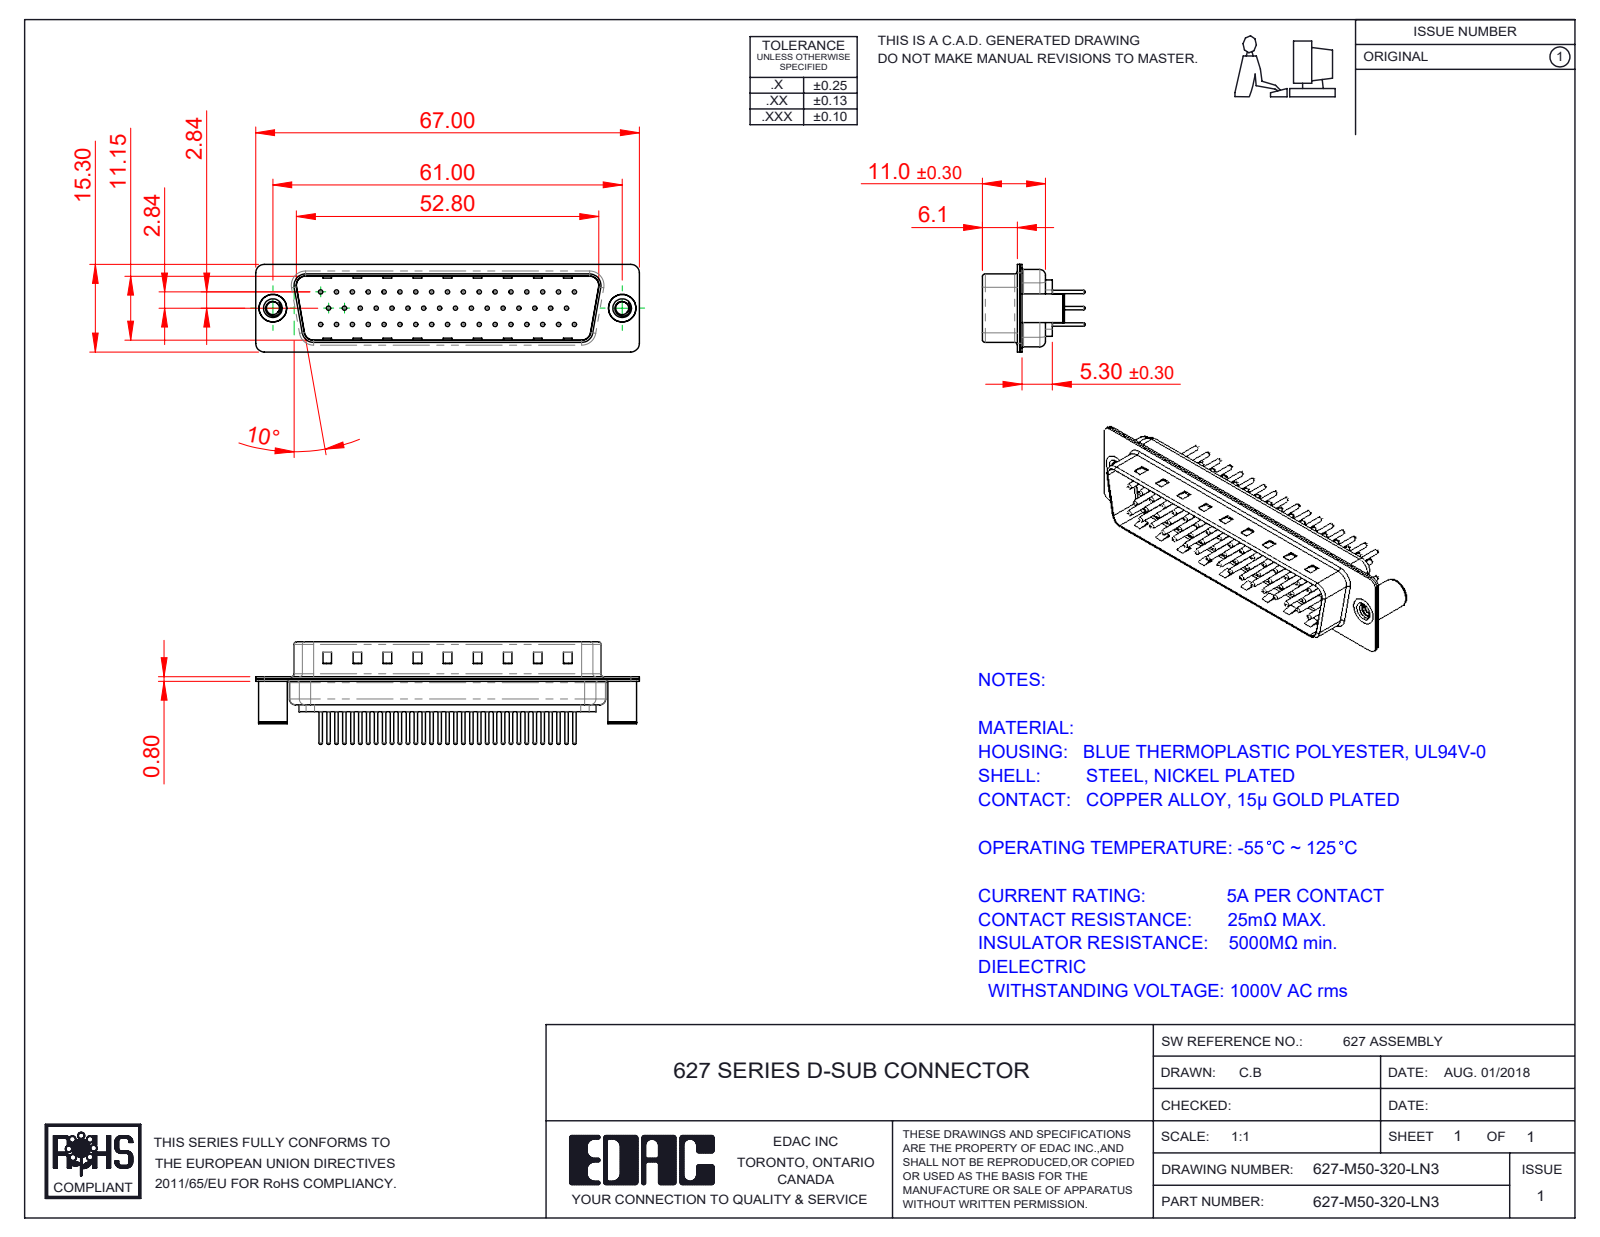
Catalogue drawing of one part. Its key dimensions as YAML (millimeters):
part_name: "627-M50-320-LN3; 627M Contact Row 3_20; 627M Shell Front_50 Contacts; 627M Contact Row 1_20 (+4 more)"
step_written_by: "SolidWorks 2020 (CONFIG_CONTROL_DESIGN)"
units: millimeters
bodies: {solids: 55, faces: 2296, planar: 553, cylindrical: 865, other: 878}
overall_size: [67, 17.9, 15.3]
volume: 4648
surface_area: 10957
round_holes:
  - {diameter: 0.75, count: 50}
  - {diameter: 1.6, count: 50}
  - {diameter: 2, count: 50}
  - {diameter: 2.26, count: 2}
  - {diameter: 3.26, count: 2}
  - {diameter: 4, count: 2}
  - {diameter: 4.8, count: 2}
round_bosses_or_shafts:
  - {diameter: 1.5, count: 50}
  - {diameter: 0.6, count: 50}
  - {diameter: 5, count: 2}
  - {diameter: 4.9, count: 2}
partial_cylinders:
  - {radius: 1.5, count: 16}
  - {radius: 2, count: 12}
  - {radius: 0.5, count: 8}
  - {radius: 1.6, count: 8}
  - {radius: 0.25, count: 4}
  - {radius: 0.6, count: 4}
  - {radius: 0.65, count: 4}
  - {radius: 0.9, count: 4}
face_to_face_distances: [0.4, 11.55, 5.7, 6.1, 0.78, 0.77, 12.33, 5.3, 12.32, 13.1]
hole_center_spacings: [3.16, 2.77, 5.54, 8.31, 11.08, 13.85, 16.62, 5.03]
